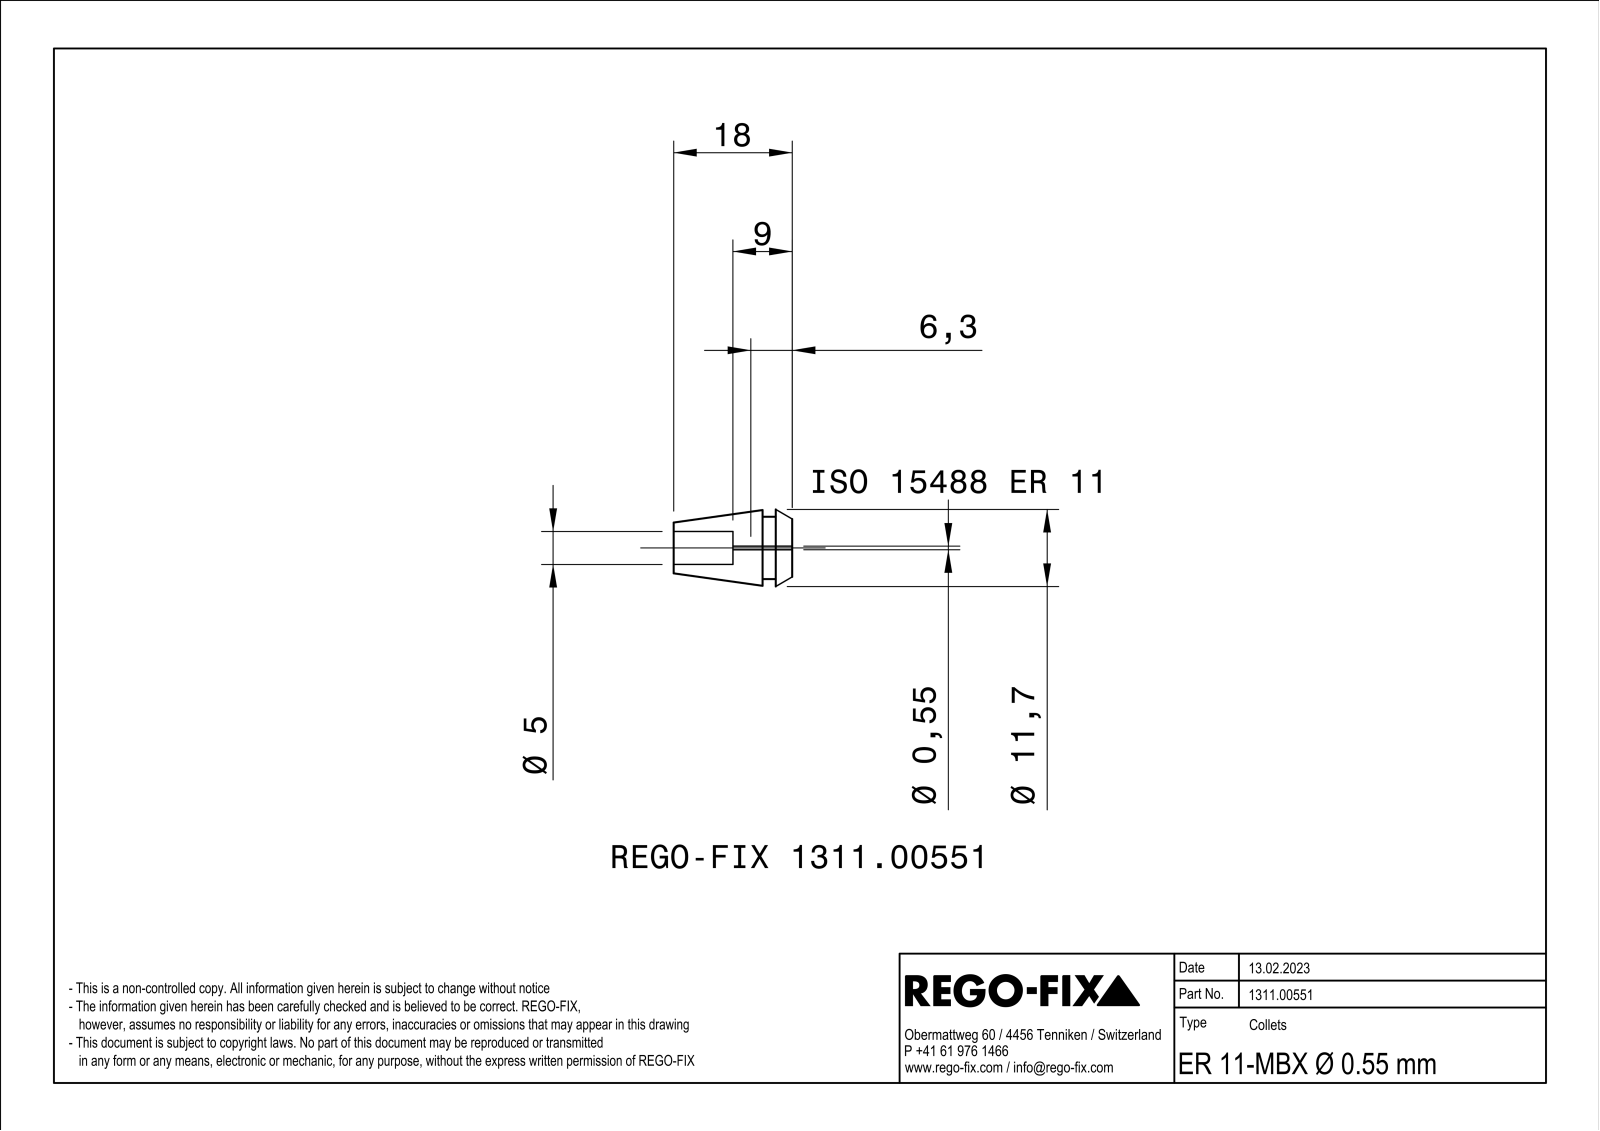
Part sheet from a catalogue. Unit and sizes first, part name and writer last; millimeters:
Units: millimetres
Overall size (bounding box): 18 × 11.41 × 11.39
Round holes (diameter × count): ⌀1.5 ×3, ⌀5 ×1
Round bosses / shafts (diameter × count): ⌀9.5 ×1
Partial cylindrical surfaces — rounded edges, fillets, slot ends (radius × count): R25 ×3, R0.28 ×1
Main face-to-face distances: 0.8, 0.51, 4.5, 9, 18, 13.5, 2.5, 2, 15.5, 6.5
Hole centre spacings: 1.7, 2.94
Volume: 992 mm³ · Surface area: 1 256 mm²
Bodies: 1 solid, 91 faces (26 planar, 19 cylindrical, 46 other)
Part name (STEP PRODUCT): NOCUT
STEP written by: SIEMENS PLM Software Solid Edge ST10 (AUTOMOTIVE_DESIGN)
